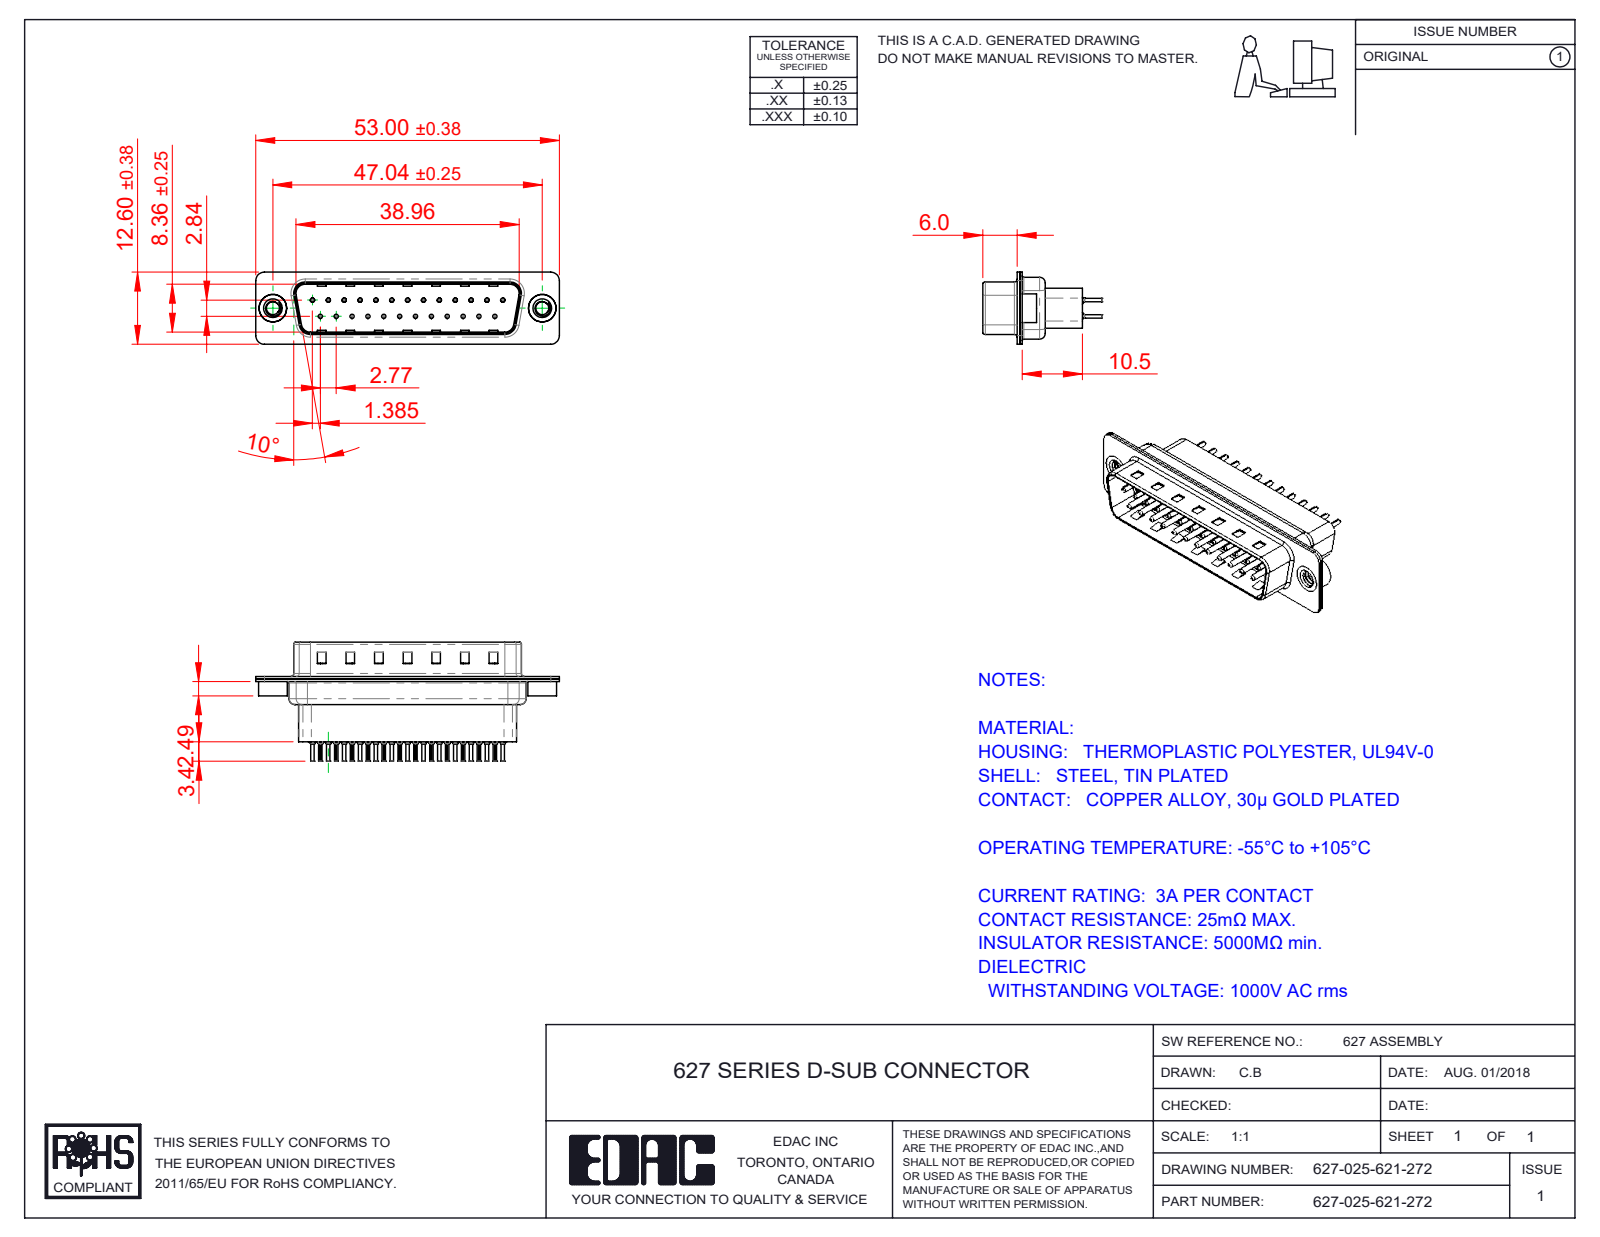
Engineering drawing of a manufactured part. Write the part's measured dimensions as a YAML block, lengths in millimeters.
part_name: "627 4-40 Threaded Rivet; 627 Contact Row 1_21H; 627 Shell Rear_25 Contacts; 627-025-621-272 (+3 more)"
step_written_by: "SolidWorks 2020 (CONFIG_CONTROL_DESIGN)"
units: millimeters
bodies: {solids: 30, faces: 2822, planar: 771, cylindrical: 1060, other: 991}
overall_size: [53, 20.8, 12.6]
volume: 3793
surface_area: 9767
round_holes:
  - {diameter: 0.2, count: 25}
  - {diameter: 0.35, count: 25}
  - {diameter: 1.1, count: 25}
  - {diameter: 1.6, count: 25}
  - {diameter: 2.26, count: 2}
  - {diameter: 4, count: 2}
  - {diameter: 4.8, count: 2}
round_bosses_or_shafts:
  - {diameter: 2, count: 25}
  - {diameter: 1.5, count: 25}
  - {diameter: 0.75, count: 25}
  - {diameter: 0.6, count: 25}
  - {diameter: 5, count: 2}
  - {diameter: 4.9, count: 2}
partial_cylinders:
  - {radius: 0.1, count: 50}
  - {radius: 1.5, count: 16}
  - {radius: 2, count: 12}
  - {radius: 0.5, count: 8}
  - {radius: 1.6, count: 8}
  - {radius: 0.25, count: 4}
  - {radius: 0.6, count: 4}
  - {radius: 0.65, count: 4}
face_to_face_distances: [0.4, 0.45, 0.82, 9.58, 0.68, 7.68, 1.5, 0.9, 1.08, 8.08]
hole_center_spacings: [3.16, 8.31, 2.77, 5.54, 11.08, 16.62, 5.03, 5.04]
